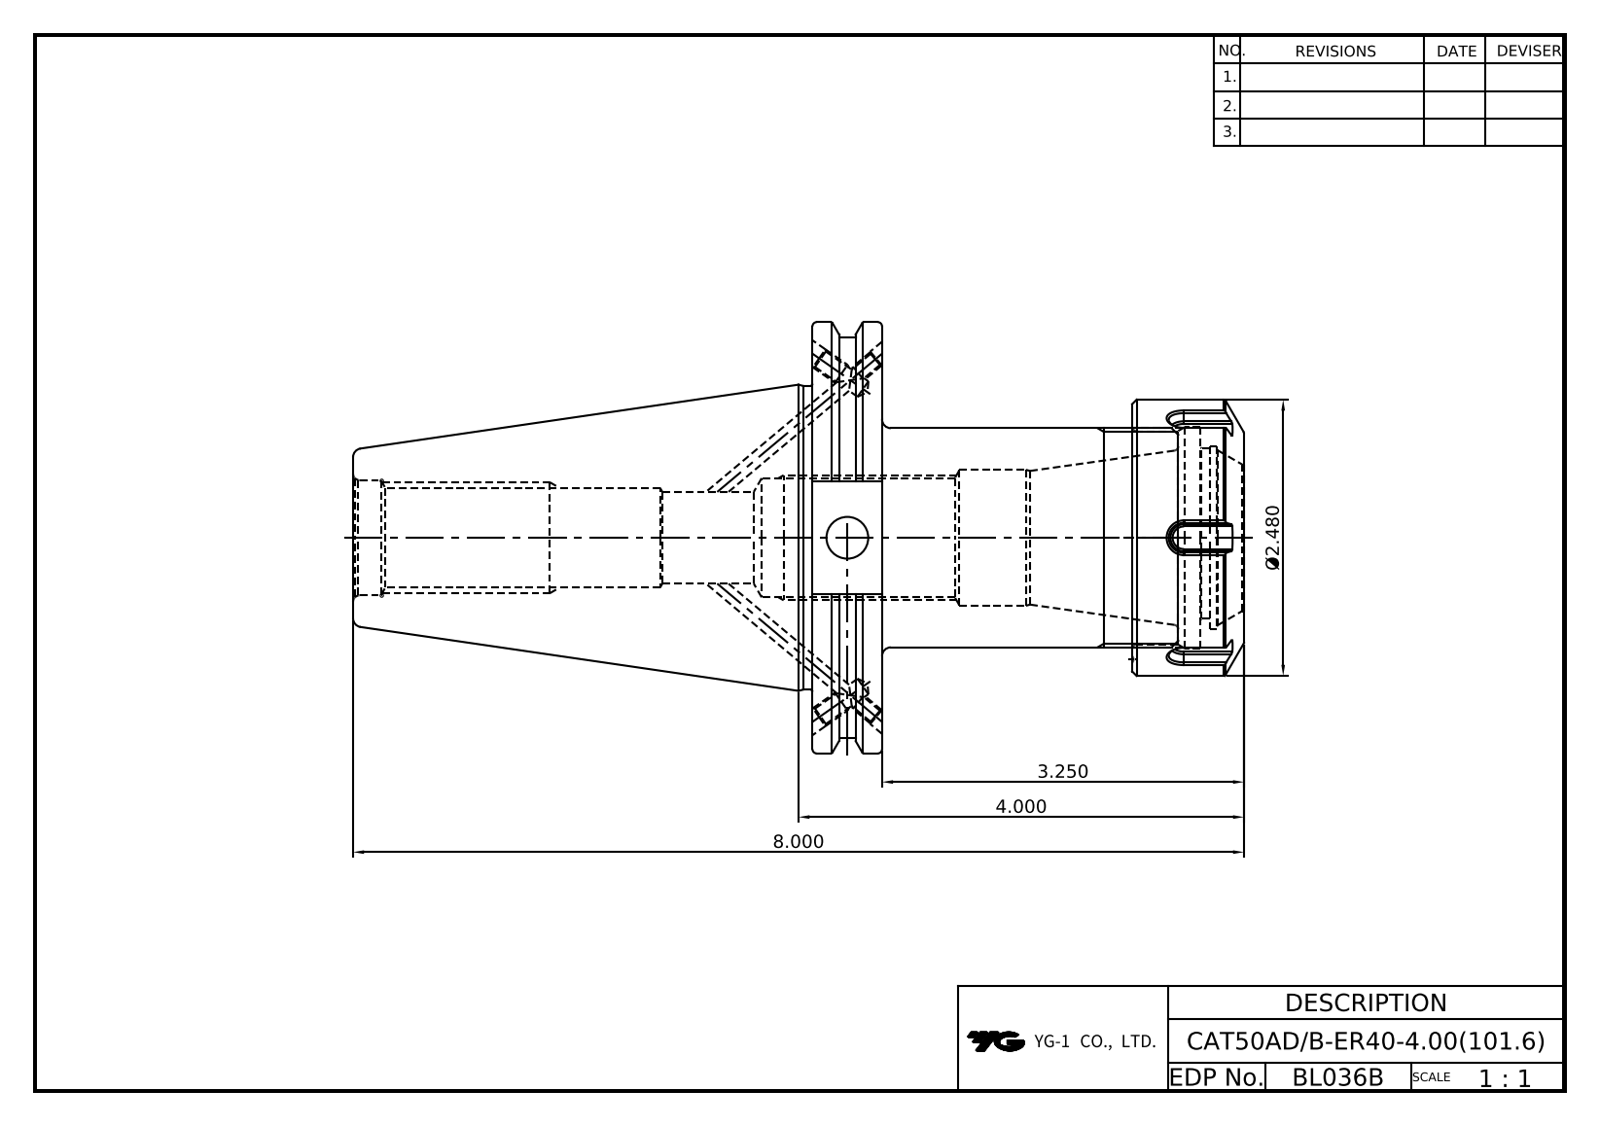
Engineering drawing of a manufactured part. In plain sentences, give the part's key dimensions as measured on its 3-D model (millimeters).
The part is named "LO-CAT50ADB-ER40-101.6_조립도; LO-CAT50ADB-ER40-101.6; ER40NUT". Its 3-D file was written by "Autodesk Inventor 2022 (AUTOMOTIVE_DESIGN)". It is 2 solids with 169 faces: 72 planar, 44 cylindrical and 53 other. Overall it measures 203.2 by 98.42 by 94.69 millimeters. Its volume is 432 172 cubic millimeters and its surface area 74 768 square millimeters. Round holes: 2 of diameter 3.24, 2 of diameter 4.13, 2 of diameter 4.2, 2 of diameter 5, 1 of diameter 1.43, 1 of diameter 9.53, 1 of diameter 21.5, 1 of diameter 21.97, 1 of diameter 26.2, 1 of diameter 26.85, 1 of diameter 31, 1 of diameter 33.5. Round bosses or shafts: 1 of diameter 98.42, 1 of diameter 91.29, 1 of diameter 69.25, 1 of diameter 63, 1 of diameter 50. Partial cylindrical surfaces (rounded edges, fillets, slot ends): 12 of radius 0.5. The main face-to-face distances are 15.88, 12, 13.5, 98.43, 82.55, 72.93, 57.05, 25.5, 84.93, 69.05. The hole center spacings are 27.75.
